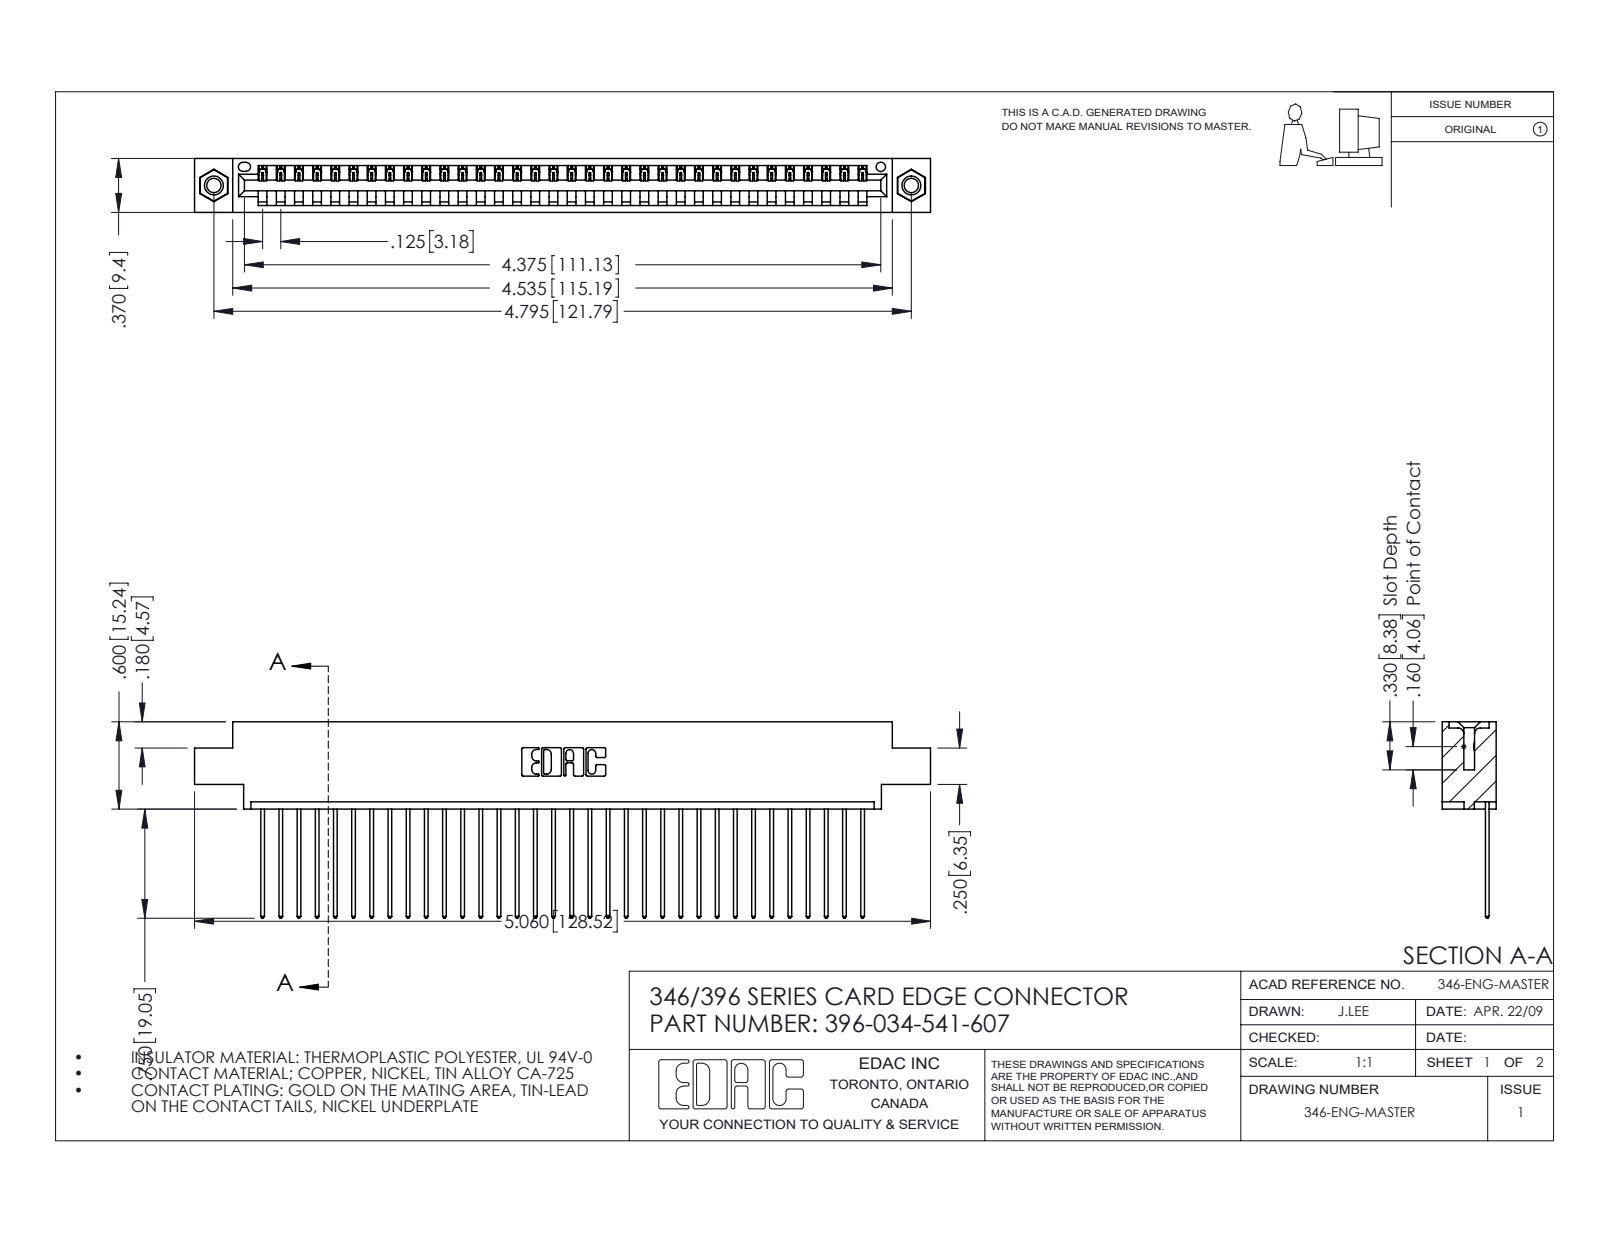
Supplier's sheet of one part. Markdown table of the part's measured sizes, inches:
| quantity | value |
| --- | --- |
| part name | 346 Part_0.170 Offset - 0.156 Dia-TI; 396-034-541-607; 345-250-001_345-250-005-103; 345-292-001_345-293-141 |
| STEP written by | SolidWorks 2016 (CONFIG_CONTROL_DESIGN) |
| units | inches |
| bodies | 37 solids, 2158 faces (1472 planar, 670 cylindrical, 16 other) |
| overall size | 5.06 × 1.35 × 0.37 |
| volume | 0.744 in³ |
| surface area | 24.83 in² |
| round holes (diameter × count) | 0.098 × 2, 0.125 × 2, 0.156 × 2, 0.064 × 1 |
| round bosses / shafts (diameter × count) | 0.155 × 2 |
| partial cylindrical surfaces (radius × count) | 0.006 × 68, 0.01 × 68, 0.01 × 22, 0.007 × 6, 0.031 × 6, 0.026 × 3, 0.031 × 2, 0.04 × 2 |
| main face-to-face distances | 0.048, 0.322, 0.37, 0.25, 0.072, 0.298, 0.025, 0.222, 0.148, 0.1 |
| hole center spacings | 0.246, 4.587, 4.795 |
